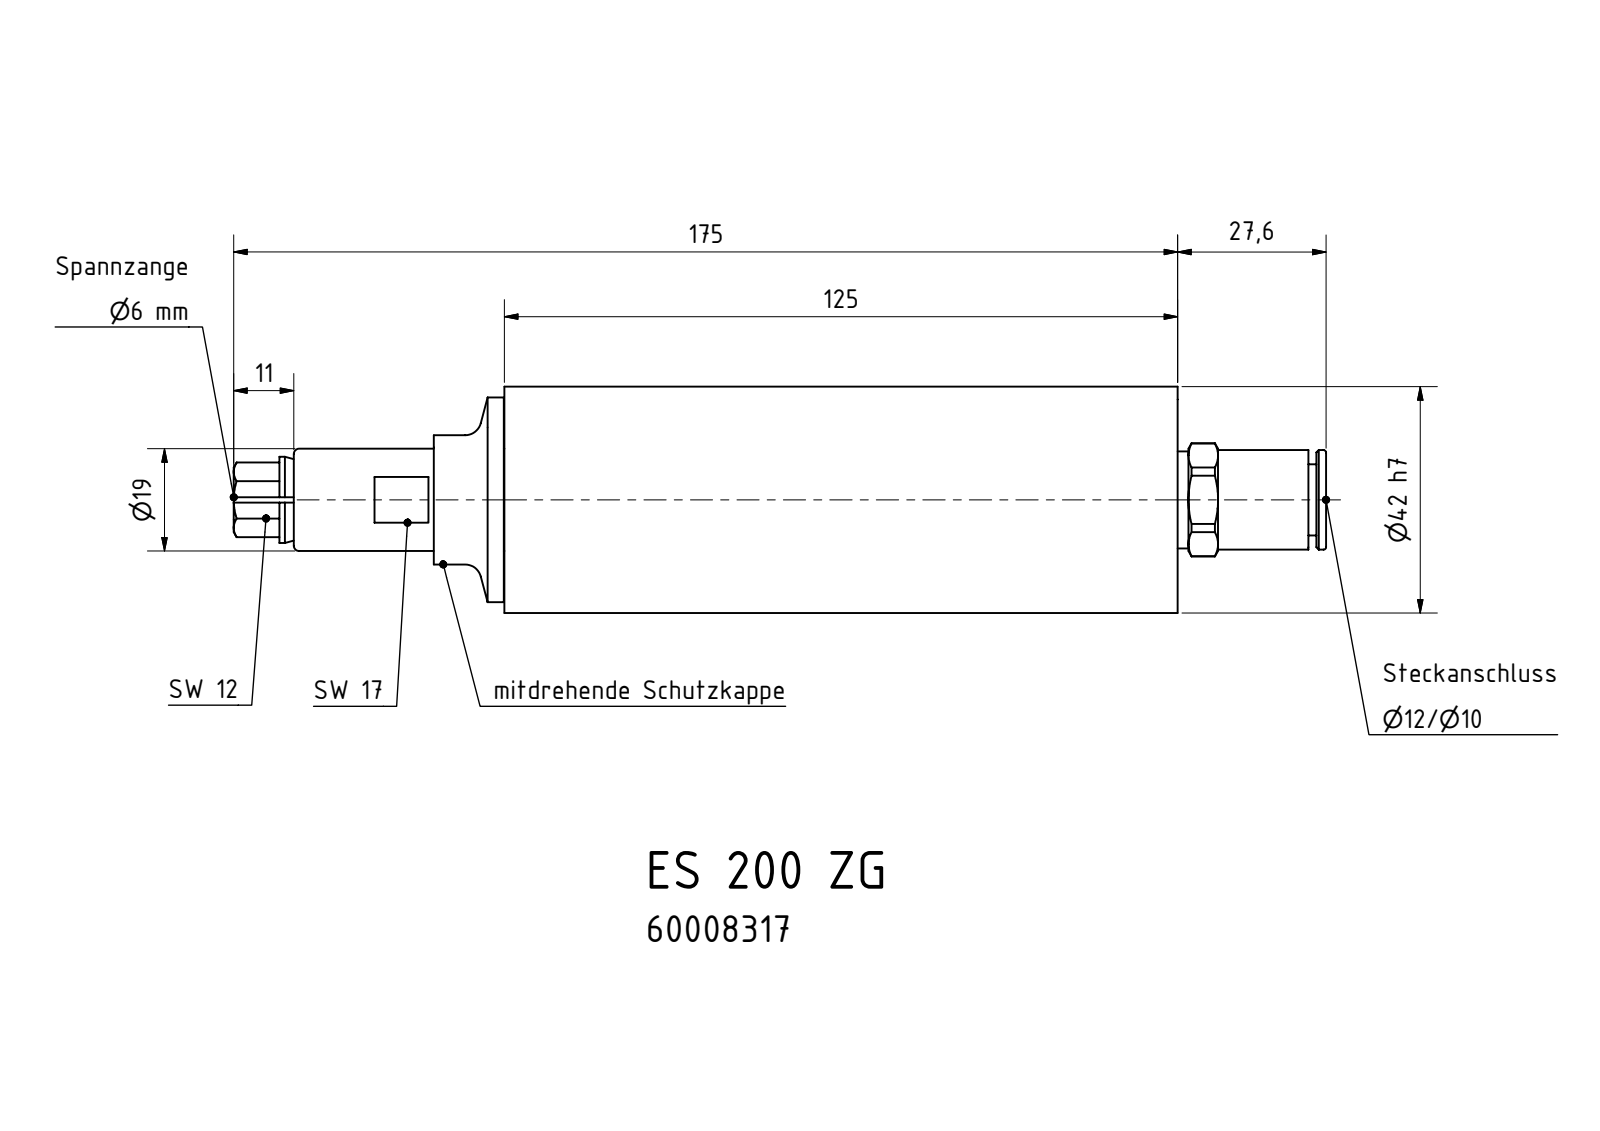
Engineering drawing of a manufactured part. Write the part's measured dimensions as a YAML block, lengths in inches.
part_name: "ES 200 ZG_60008317"
step_written_by: "Autodesk Inventor 2008 (CONFIG_CONTROL_DESIGN)"
units: inches
bodies: {solids: 1, faces: 138, planar: 66, cylindrical: 34, other: 38}
overall_size: [7.985, 1.654, 1.654]
volume: 11.74
surface_area: 45.87
round_holes:
  - {diameter: 0.236, count: 1}
  - {diameter: 0.335, count: 1}
  - {diameter: 0.472, count: 1}
  - {diameter: 0.622, count: 1}
  - {diameter: 0.768, count: 1}
  - {diameter: 1.421, count: 1}
round_bosses_or_shafts:
  - {diameter: 1.654, count: 1}
  - {diameter: 1.496, count: 1}
  - {diameter: 1.417, count: 1}
  - {diameter: 0.945, count: 1}
  - {diameter: 0.748, count: 1}
  - {diameter: 0.728, count: 1}
  - {diameter: 0.709, count: 1}
  - {diameter: 0.63, count: 1}
partial_cylinders:
  - {radius: 0.591, count: 3}
  - {radius: 0.188, count: 1}
  - {radius: 0.413, count: 1}
face_to_face_distances: [4.925, 4.937, 0.016, 4.921, 0.512, 0.039, 0.138, 0.61, 0.098, 0.472]
